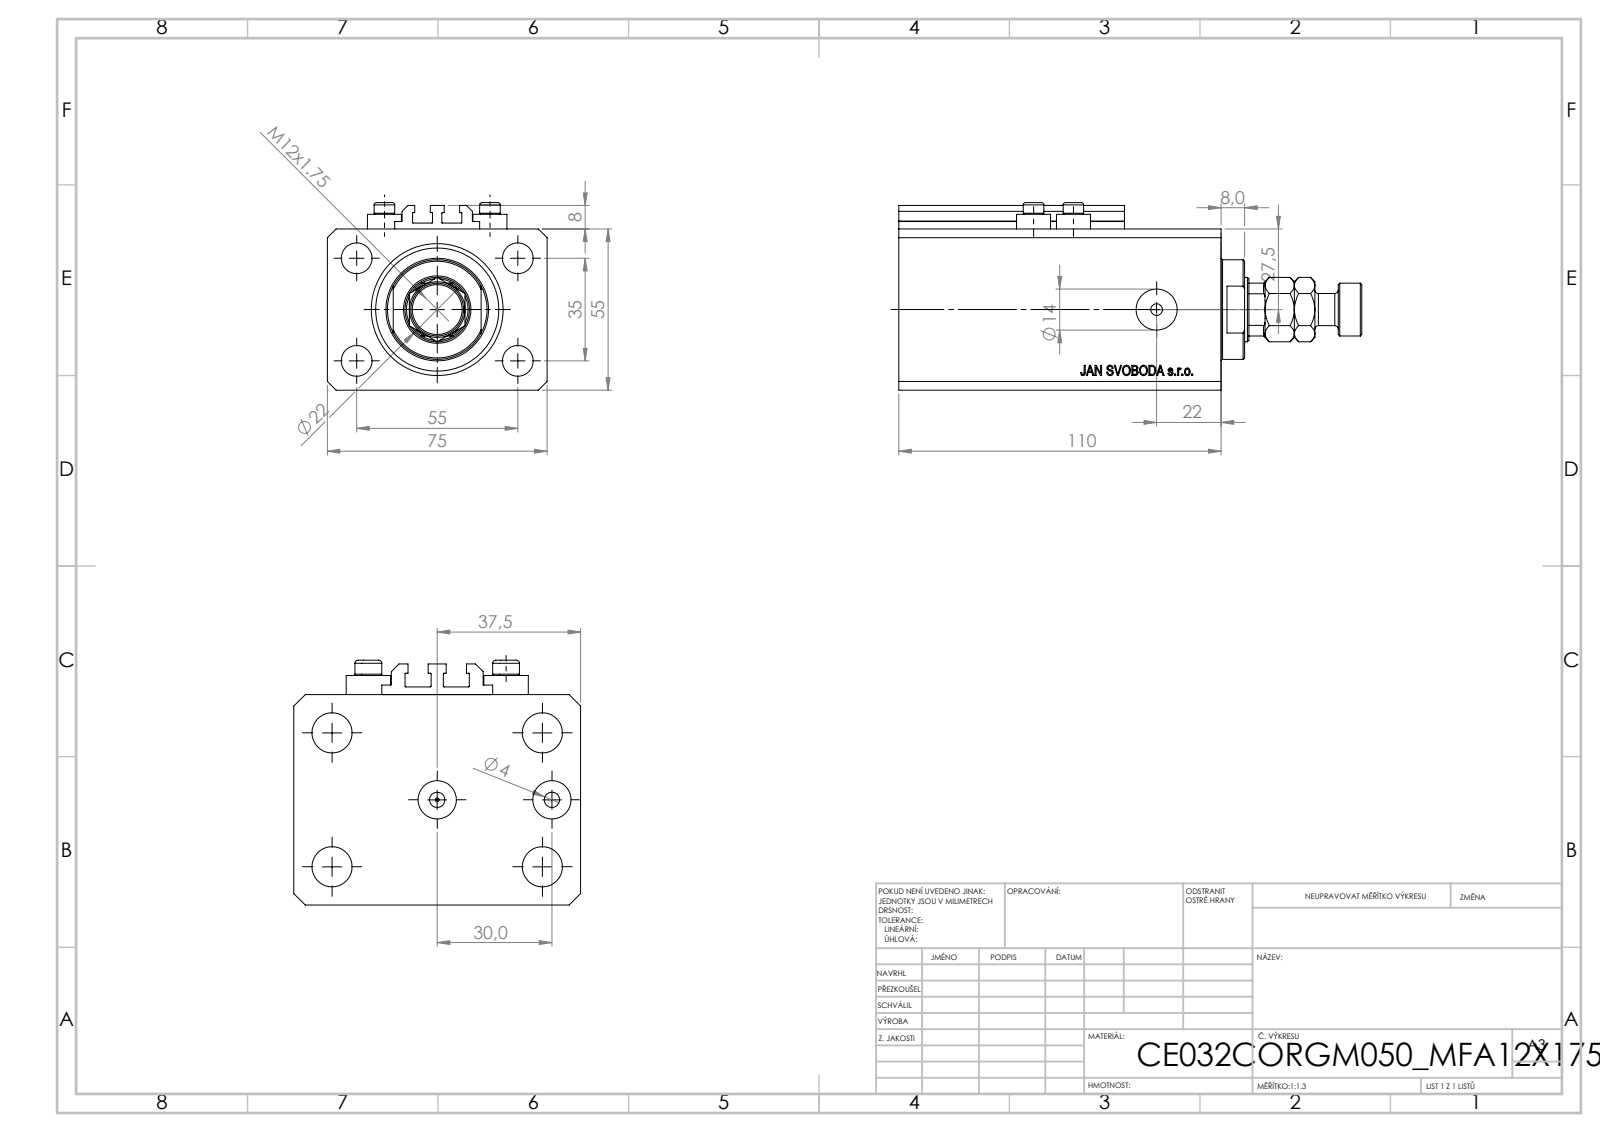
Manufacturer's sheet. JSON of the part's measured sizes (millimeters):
{"part_name": "MFA; V250CE_C_VCP; ALLEN BOLT V250CE; V250CE_VC_C (+1 more)", "step_written_by": "SolidWorks 2019 (CONFIG_CONTROL_DESIGN)", "units": "millimeters", "bodies": {"solids": 9, "faces": 1090, "planar": 520, "cylindrical": 92, "other": 478}, "overall_size": [158, 75, 64], "volume_mm3": 416515, "surface_area_mm2": 94305, "round_holes": [[4, 8], [10.5, 5], [10, 2], [14, 2], [1.25, 1], [22, 1], [32, 1], [45, 1]], "round_bosses_or_shafts": [[11.6, 4], [7, 4], [34, 1], [18, 1], [11, 1]], "partial_cylinders_radius": [[0.2, 10], [10.5, 1]], "face_to_face_distances": [55, 75, 110, 15, 95, 9.9, 85.1, 100.1, 2.5, 8], "hole_center_spacings": [32.6, 13.6, 17.68, 35, 36, 38.48, 55, 60.1]}
